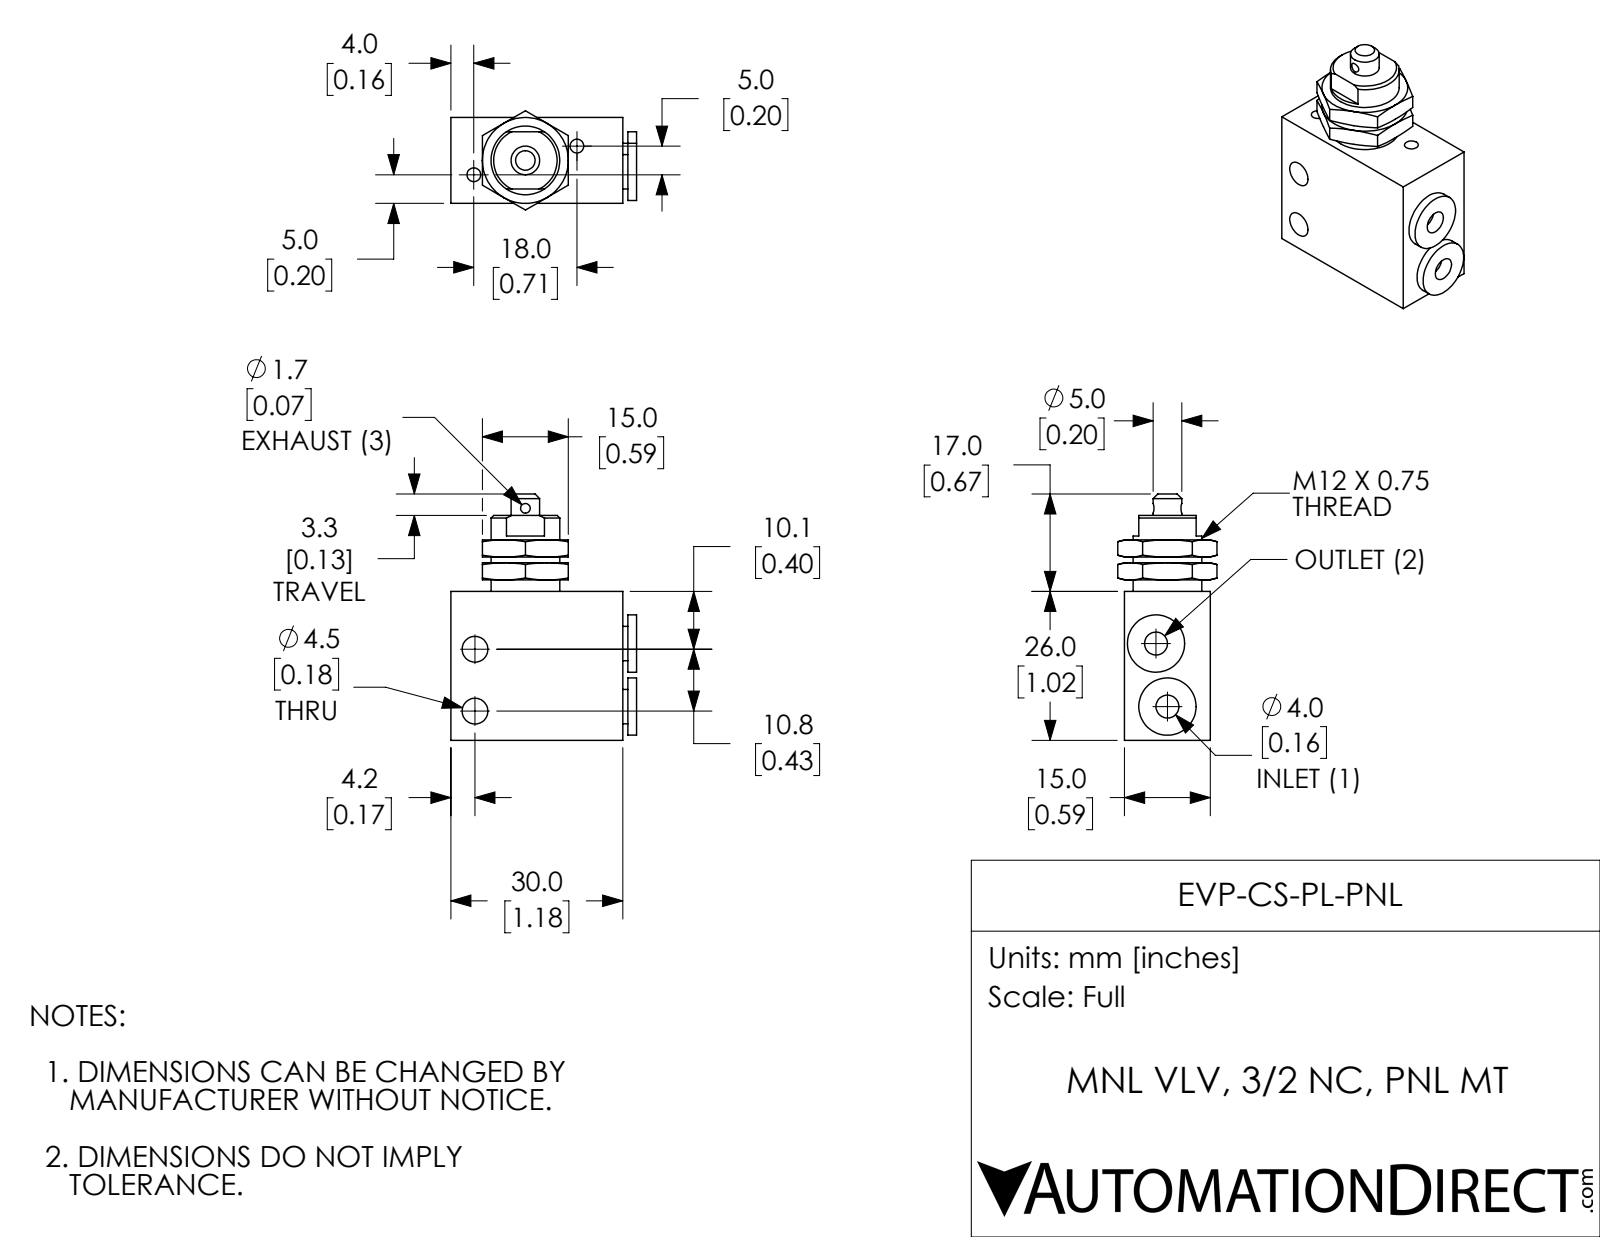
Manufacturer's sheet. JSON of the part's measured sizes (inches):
{"part_name": "EVP-CS-PL-PNL", "step_written_by": "SolidWorks 2017 (AUTOMOTIVE_DESIGN)", "units": "inches", "bodies": {"solids": 1, "faces": 97, "planar": 36, "cylindrical": 30, "other": 31}, "overall_size": [1.693, 1.276, 0.682], "volume_in3": 0.819, "surface_area_in2": 7.758, "round_holes": [[0.094, 2], [0.157, 2], [0.177, 2], [0.067, 1]], "round_bosses_or_shafts": [[0.394, 2], [0.236, 2], [0.472, 1], [0.197, 1]], "face_to_face_distances": [0.591, 1.181, 1.024, 0.157, 1.276, 0.094, 0.118, 1.217, 0.035, 0.059], "hole_center_spacings": [0.425, 0.44, 0.735, 1.029, 1.436]}
